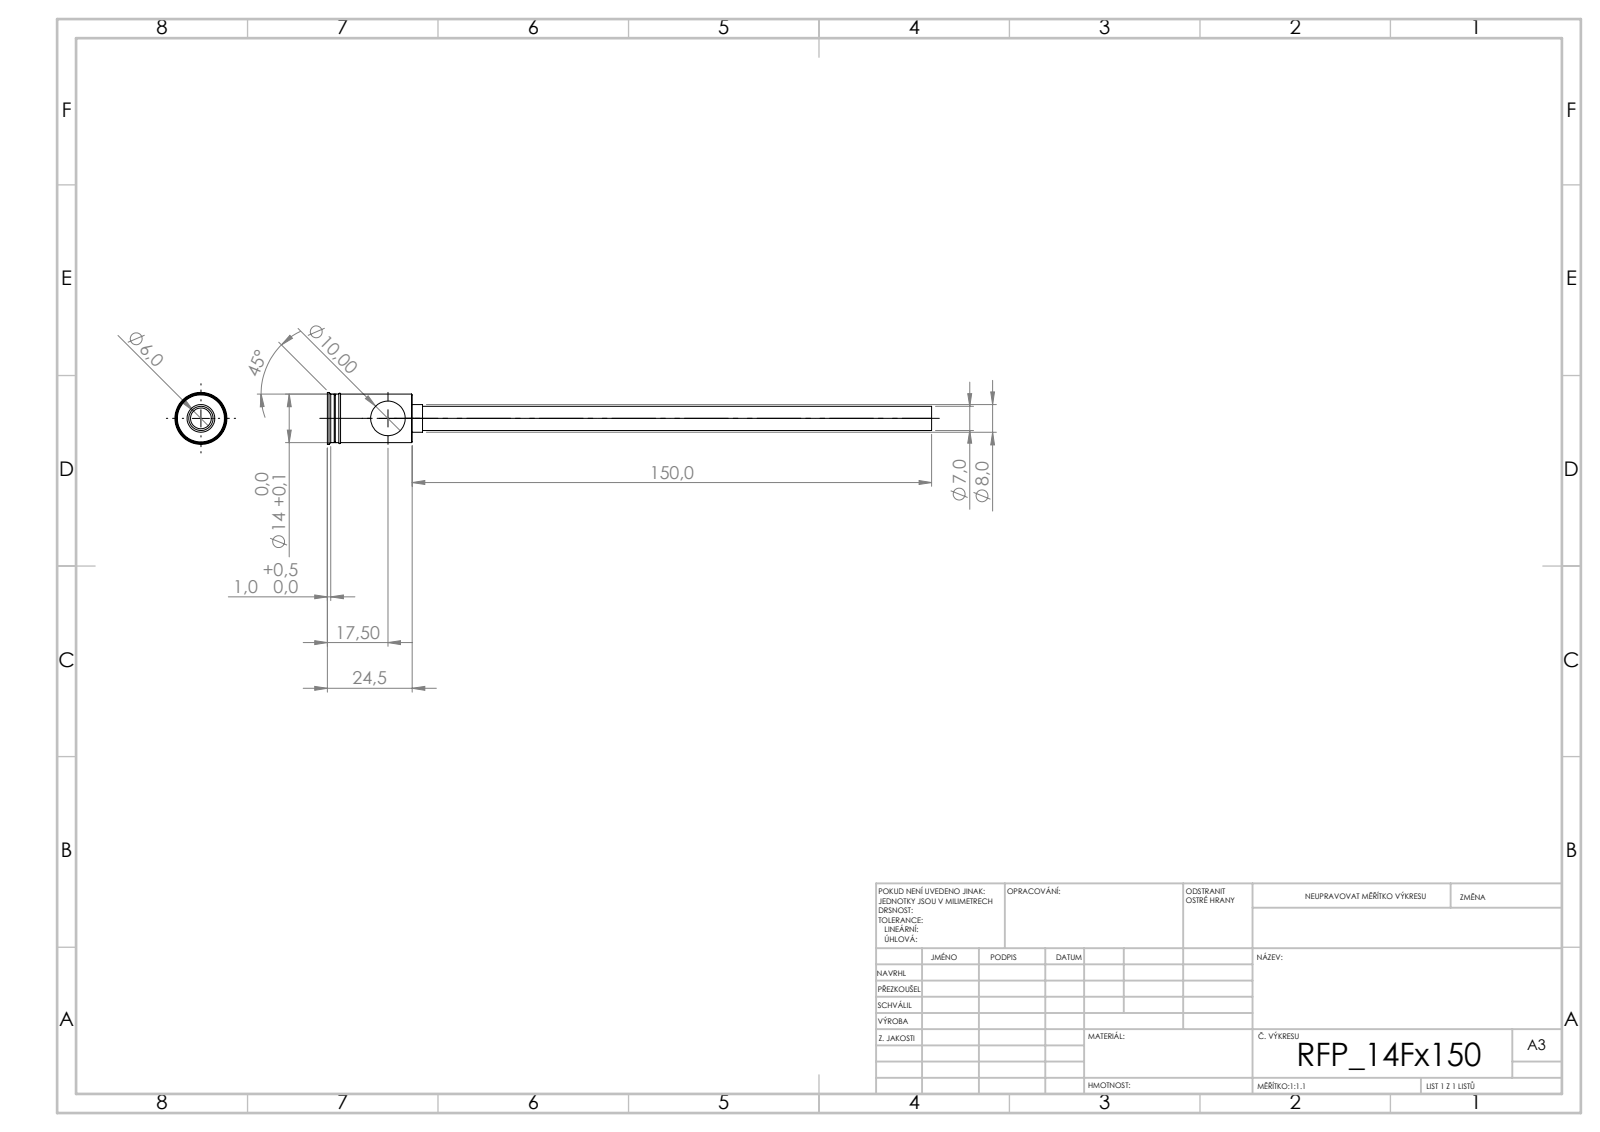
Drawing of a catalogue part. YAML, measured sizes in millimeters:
step_written_by: "SolidWorks 2019 (CONFIG_CONTROL_DESIGN)"
units: millimeters
bodies: {solids: 1, faces: 44, planar: 20, cylindrical: 16, other: 8}
overall_size: [174.5, 15, 15]
volume: 4117
surface_area: 7843
round_holes:
  - {diameter: 6, count: 1}
  - {diameter: 10, count: 1}
round_bosses_or_shafts:
  - {diameter: 15, count: 1}
  - {diameter: 14, count: 1}
  - {diameter: 8, count: 1}
  - {diameter: 7, count: 1}
face_to_face_distances: [24.5, 22.5, 2, 9.4, 22.2, 2.3, 3, 25.2, 25.5, 27.5]
